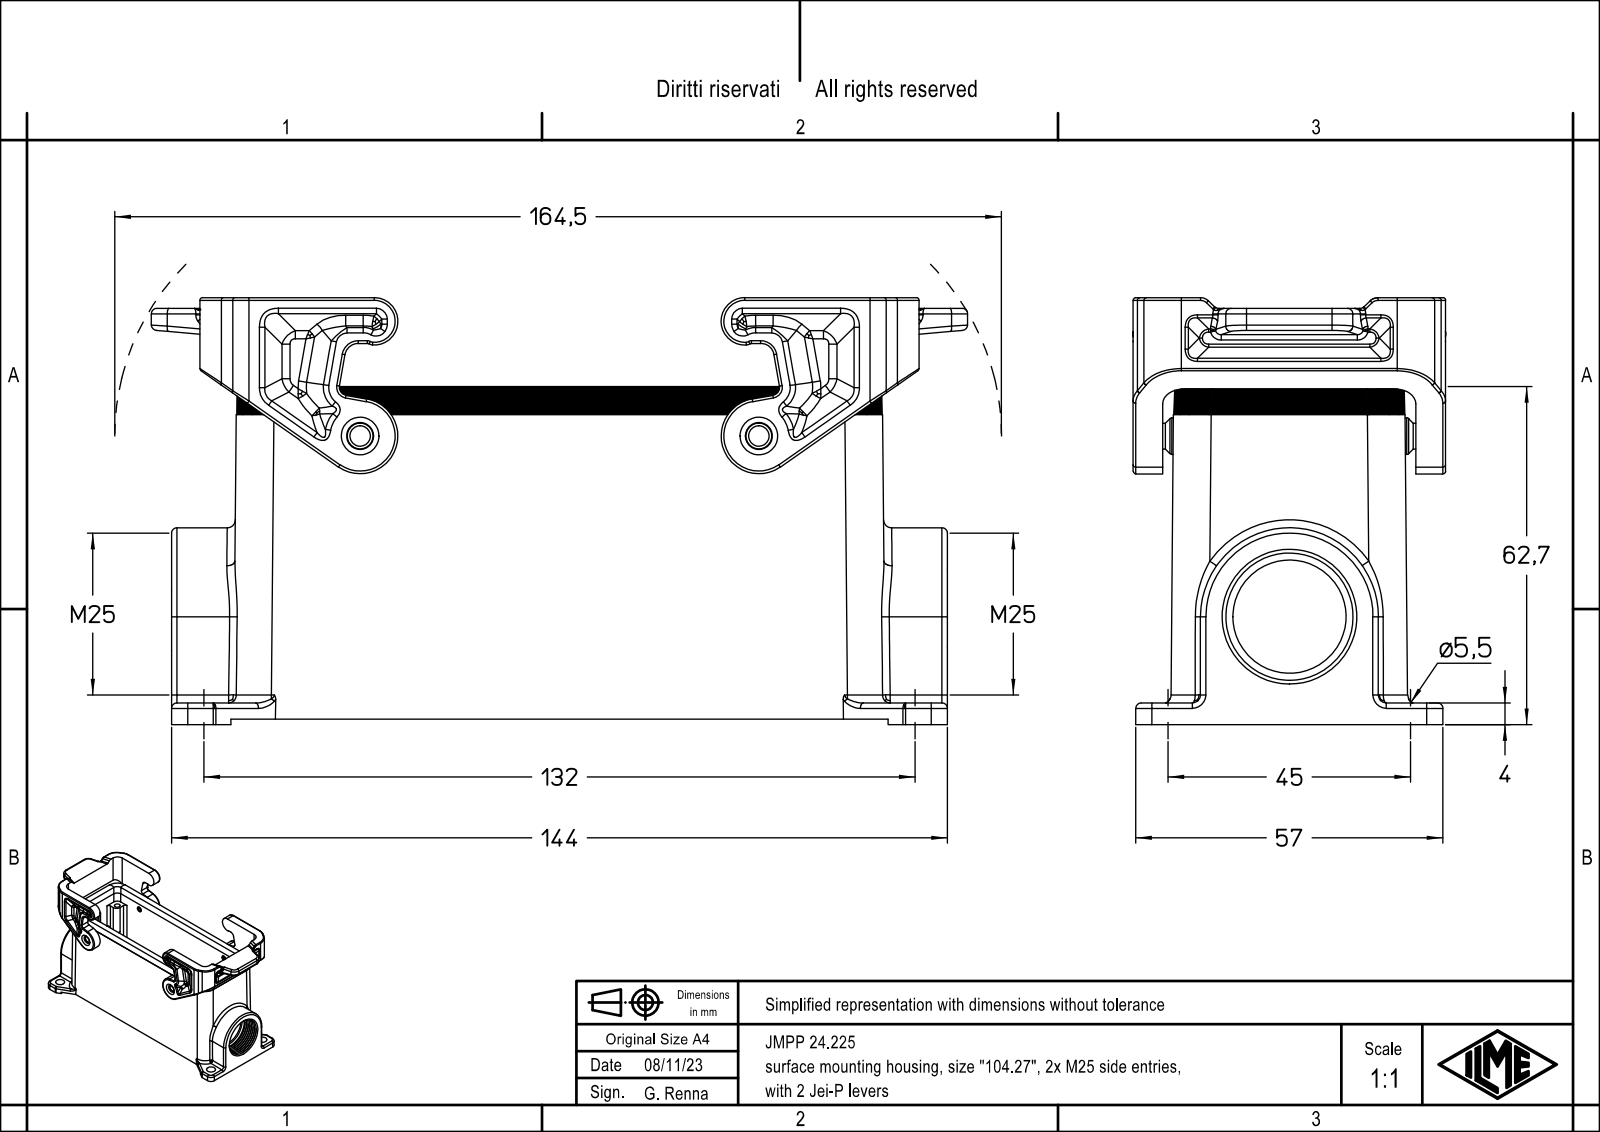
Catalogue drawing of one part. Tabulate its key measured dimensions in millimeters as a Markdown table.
| quantity | value |
| --- | --- |
| part name | JMPP 24.225 |
| STEP written by | Creo Elements/Direct Modeling 20.1B 02-Apr-2019 (C) Parametric Technology GmbH (AUTOMOTIVE_DESIGN) |
| units | millimeters |
| bodies | 1 solid, 892 faces (170 planar, 314 cylindrical, 408 other) |
| overall size | 151.5 × 79.2 × 58.08 |
| volume | 143 186 mm³ |
| surface area | 65 603 mm² |
| round holes (diameter × count) | 3 × 4, 3.5 × 4, 5.5 × 4, 4.8 × 2, 21 × 1, 23.6 × 1 |
| round bosses / shafts (diameter × count) | 6.8 × 2 |
| partial cylindrical surfaces (radius × count) | 0.5 × 50, 1 × 48, 3 × 38, 2 × 24, 1.5 × 16, 4 × 12, 6 × 12, 7 × 10 |
| main face-to-face distances | 3, 47, 7, 1, 4, 10.25, 133.75, 38.9, 5.5, 52.5 |
| hole center spacings | 16.64, 38.63, 118.34, 123.37, 27, 45, 104, 107.45 |
